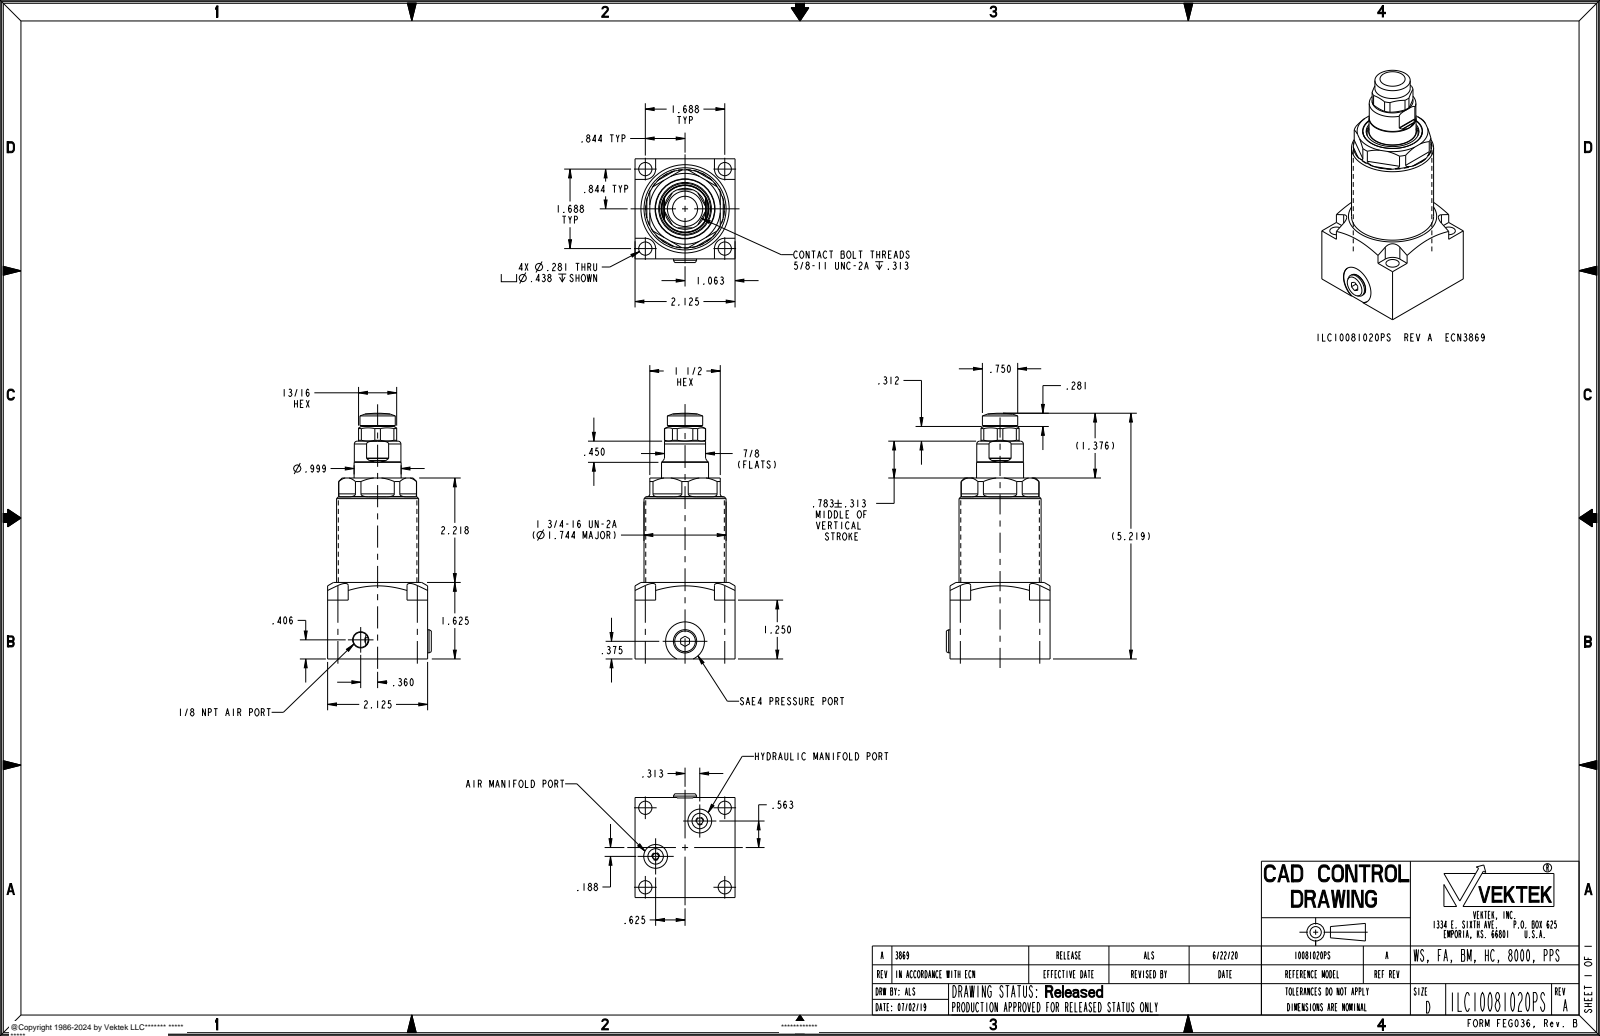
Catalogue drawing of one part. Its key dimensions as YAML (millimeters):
part_name: "ILC10081020PS"
step_written_by: "PRO/ENGINEER BY PARAMETRIC TECHNOLOGY CORPORATION, 2013320 (CONFIG_CONTROL_DESIGN)"
units: millimeters
bodies: {solids: 2, faces: 203, planar: 68, cylindrical: 77, other: 58}
overall_size: [132.6, 56, 54]
volume: 205000
surface_area: 39630
round_holes:
  - {diameter: 7.1, count: 4}
  - {diameter: 3.5, count: 2}
  - {diameter: 4.2, count: 2}
  - {diameter: 8.3, count: 2}
  - {diameter: 12.8, count: 2}
  - {diameter: 3.2, count: 1}
  - {diameter: 10, count: 1}
  - {diameter: 21, count: 1}
  - {diameter: 26.4, count: 1}
  - {diameter: 28.4, count: 1}
  - {diameter: 31.8, count: 1}
round_bosses_or_shafts:
  - {diameter: 44.3, count: 1}
  - {diameter: 42.4, count: 1}
  - {diameter: 31.9, count: 1}
  - {diameter: 25.4, count: 1}
  - {diameter: 25.1, count: 1}
  - {diameter: 11.1, count: 1}
  - {diameter: 11.1, count: 1}
partial_cylinders:
  - {radius: 1.6, count: 6}
  - {radius: 0.5, count: 4}
  - {radius: 5.6, count: 4}
  - {radius: 11.1, count: 1}
  - {radius: 21, count: 1}
face_to_face_distances: [54, 38, 97.6, 31.8, 65.9, 11.1, 42.9, 8, 46, 41.3]
hole_center_spacings: [30.3, 42.9, 60.6, 15.3, 16.4, 16.6, 17.6, 26.8]
